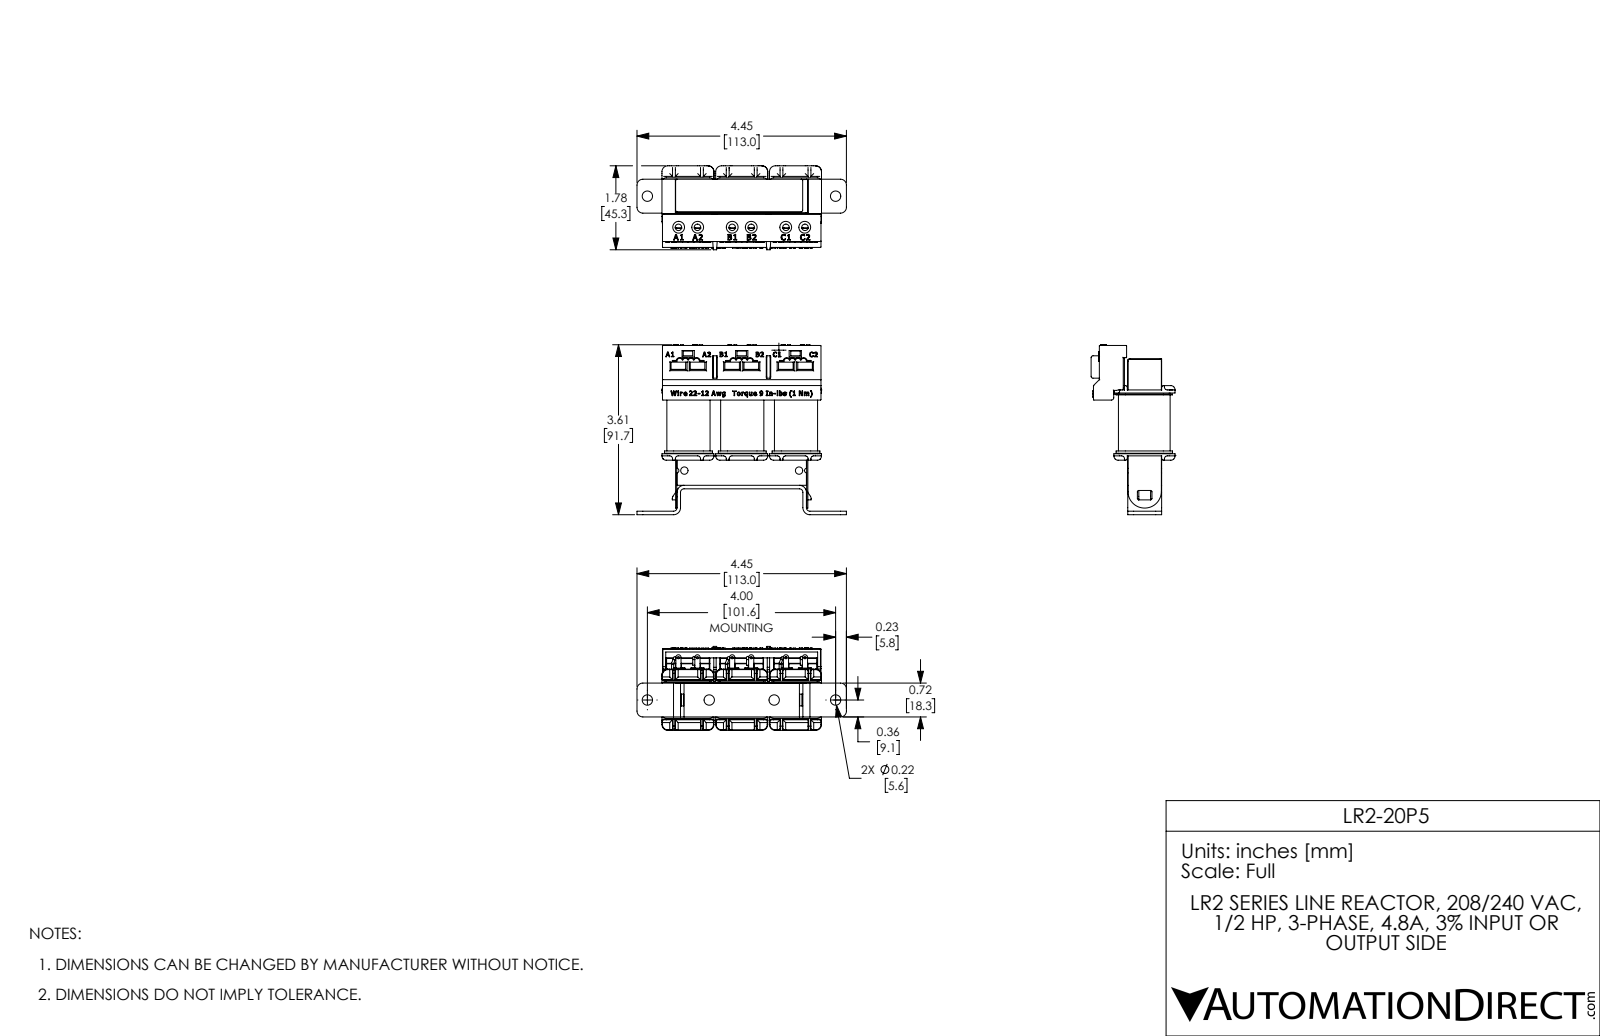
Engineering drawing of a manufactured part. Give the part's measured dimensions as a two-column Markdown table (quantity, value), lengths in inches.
| quantity | value |
| --- | --- |
| part name | KDRMA Model CoordFix XT (106686DG) Rep3 ext 1Bc1 Reduced 2r2 comb |
| STEP written by | SolidWorks 2017 (AUTOMOTIVE_DESIGN) |
| units | inches |
| bodies | 31 solids, 3278 faces (1790 planar, 811 cylindrical, 677 other) |
| overall size | 4.45 × 3.61 × 1.784 |
| volume | 8.424 in³ |
| surface area | 102.2 in² |
| round holes (diameter × count) | 0.048 × 6, 0.138 × 6, 0.25 × 6, 0.156 × 4, 0.22 × 4 |
| round bosses / shafts (diameter × count) | 0.045 × 11, 0.175 × 4, 0.045 × 4, 0.175 × 2 |
| partial cylindrical surfaces (radius × count) | 0.01 × 172, 0.06 × 27, 0.05 × 16, 0.125 × 16, 0.09 × 15, 0.045 × 14, 0.059 × 12, 0.075 × 12 |
| main face-to-face distances | 0.918, 1.143, 2.061, 0.07, 0.625, 0.722, 2.005, 0.025, 0.074, 0.07 |
| hole center spacings | 1.143, 0.404, 1.137, 1.167, 0.237, 0.239, 0.469, 0.739 |
